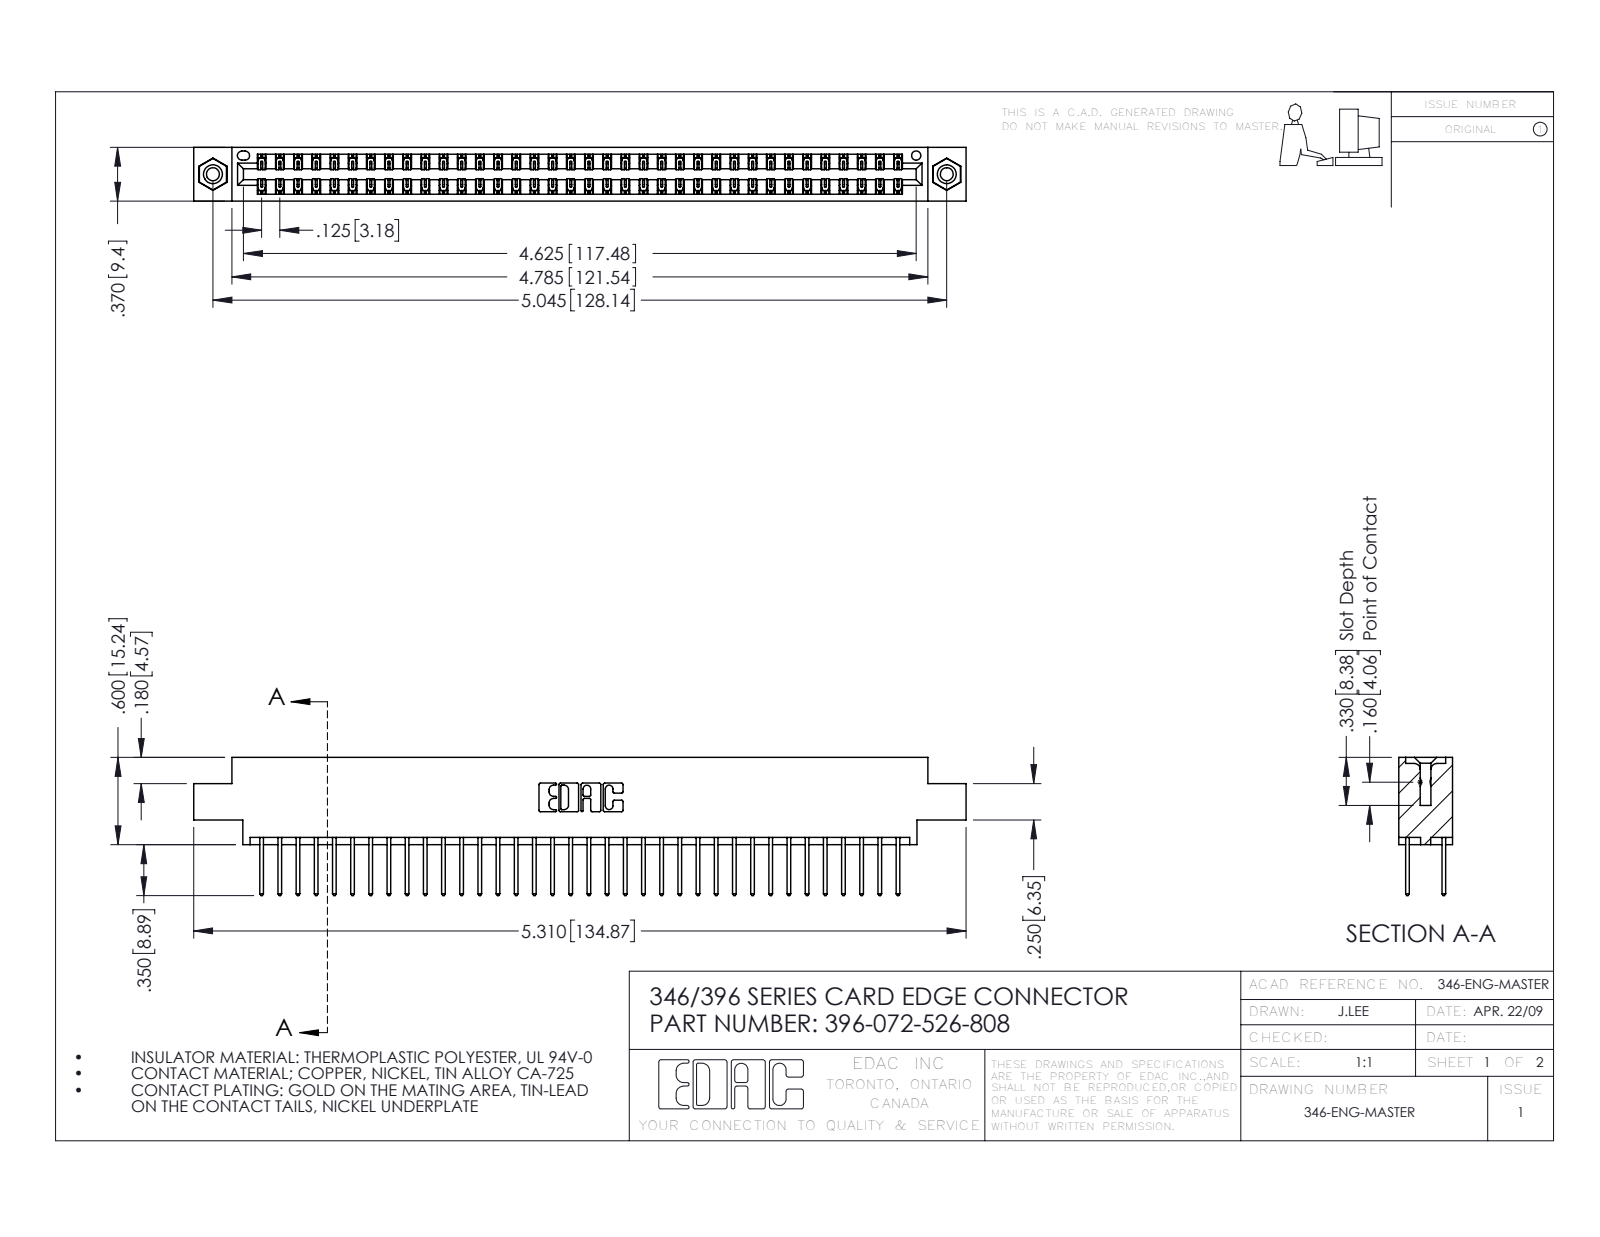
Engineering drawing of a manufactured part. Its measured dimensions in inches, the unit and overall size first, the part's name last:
Units: inches
Overall size (bounding box): 5.31 × 0.95 × 0.37
Round holes (diameter × count): ⌀0.089 ×2, ⌀0.125 ×2, ⌀0.156 ×2, ⌀0.064 ×1
Round bosses / shafts (diameter × count): ⌀0.155 ×2
Partial cylindrical surfaces — rounded edges, fillets, slot ends (radius × count): R0.006 ×108, R0.01 ×72, R0.01 ×22, R0.007 ×6, R0.031 ×6, R0.026 ×3, R0.014 ×2, R0.022 ×2
Main face-to-face distances: 0.048, 0.322, 0.25, 0.37, 0.072, 0.298, 0.025, 0.275, 0.222, 0.148
Hole centre spacings: 0.246, 4.836, 5.045
Volume: 0.797 in³ · Surface area: 28.81 in²
Bodies: 75 solids, 3930 faces (2632 planar, 1282 cylindrical, 16 other)
Part name (STEP PRODUCT): 346 Part_0.170 Offset - 0.156 Dia-TI; 345-292-001_345-293-126; 345-250-001_345-250-003-102; 396-072-526-808
STEP written by: SolidWorks 2016 (CONFIG_CONTROL_DESIGN)
